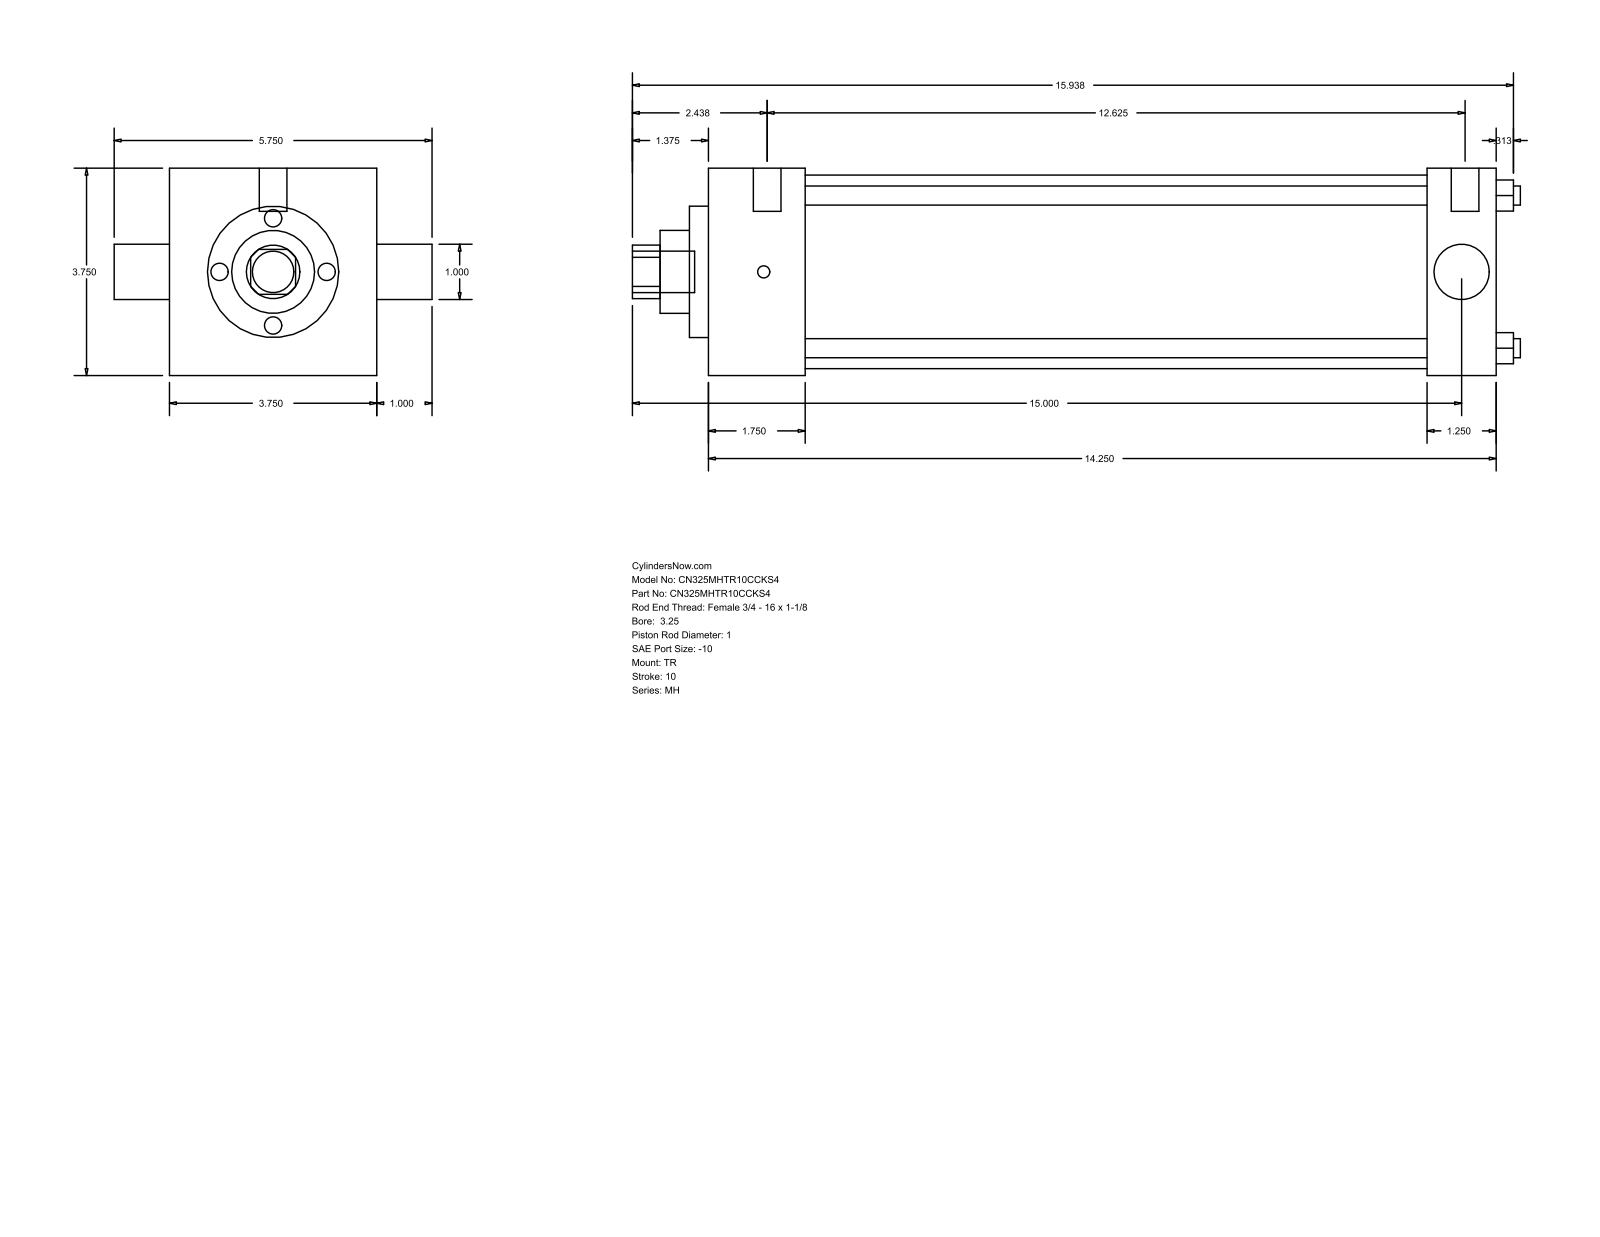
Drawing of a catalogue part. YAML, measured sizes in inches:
part_name: "MH_TR__0325_1"
step_written_by: "GSSL Pune (CONFIG_CONTROL_DESIGN)"
units: inches
bodies: {solids: 0, faces: 86, planar: 61, cylindrical: 25, other: 0}
overall_size: [16.063, 5.75, 3.75]
round_holes:
  - {diameter: 0.345, count: 4}
  - {diameter: 1, count: 2}
  - {diameter: 1.5, count: 1}
  - {diameter: 2.375, count: 1}
  - {diameter: 3.5, count: 1}
round_bosses_or_shafts:
  - {diameter: 0.219, count: 3}
  - {diameter: 0.5, count: 2}
  - {diameter: 0.75, count: 1}
partial_cylinders:
  - {radius: 0.484, count: 1}
face_to_face_distances: [3.75, 14.25, 1.75, 13, 11.25, 12.5, 1.25, 0.344, 2.094, 13.344]
hole_center_spacings: [1.952, 2.76, 3.903]
